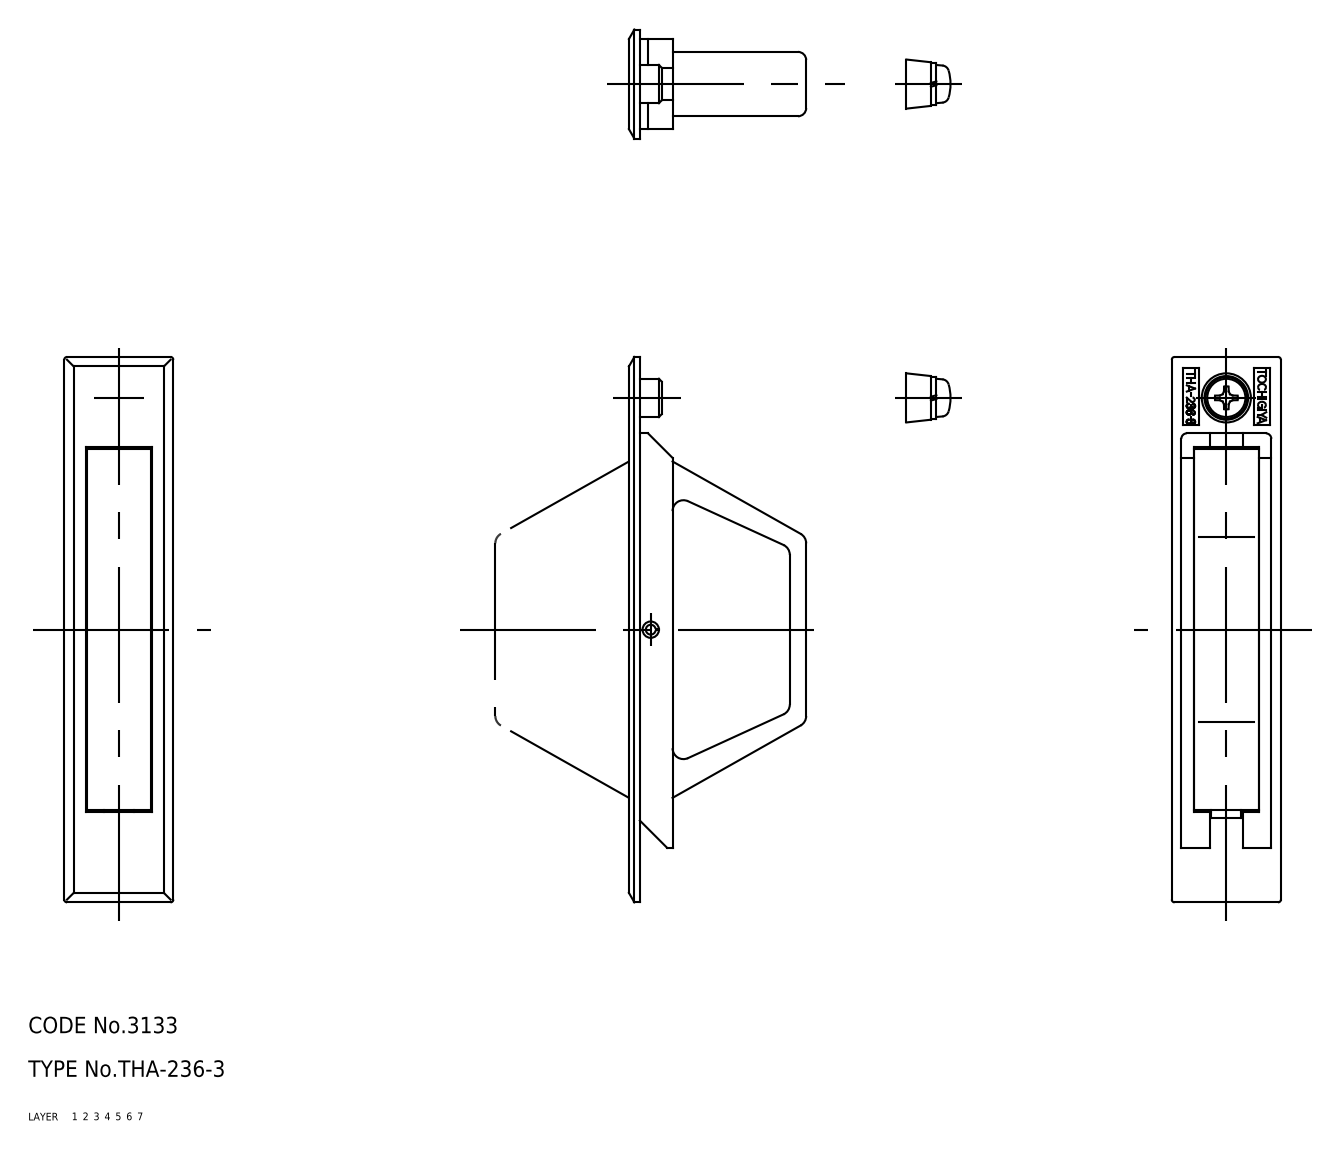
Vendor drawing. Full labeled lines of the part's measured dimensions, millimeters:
Part name (STEP PRODUCT): screw; pull; pin; bracket (+2 more)
STEP written by: CADfix (AUTOMOTIVE_DESIGN)
Units: millimetres
Bodies: 5 solids, 170 faces (0 planar, 0 cylindrical, 170 other)
Overall size (bounding box): 100 × 32.5 × 20
Volume: 12 886 mm³ · Surface area: 11 808 mm²
